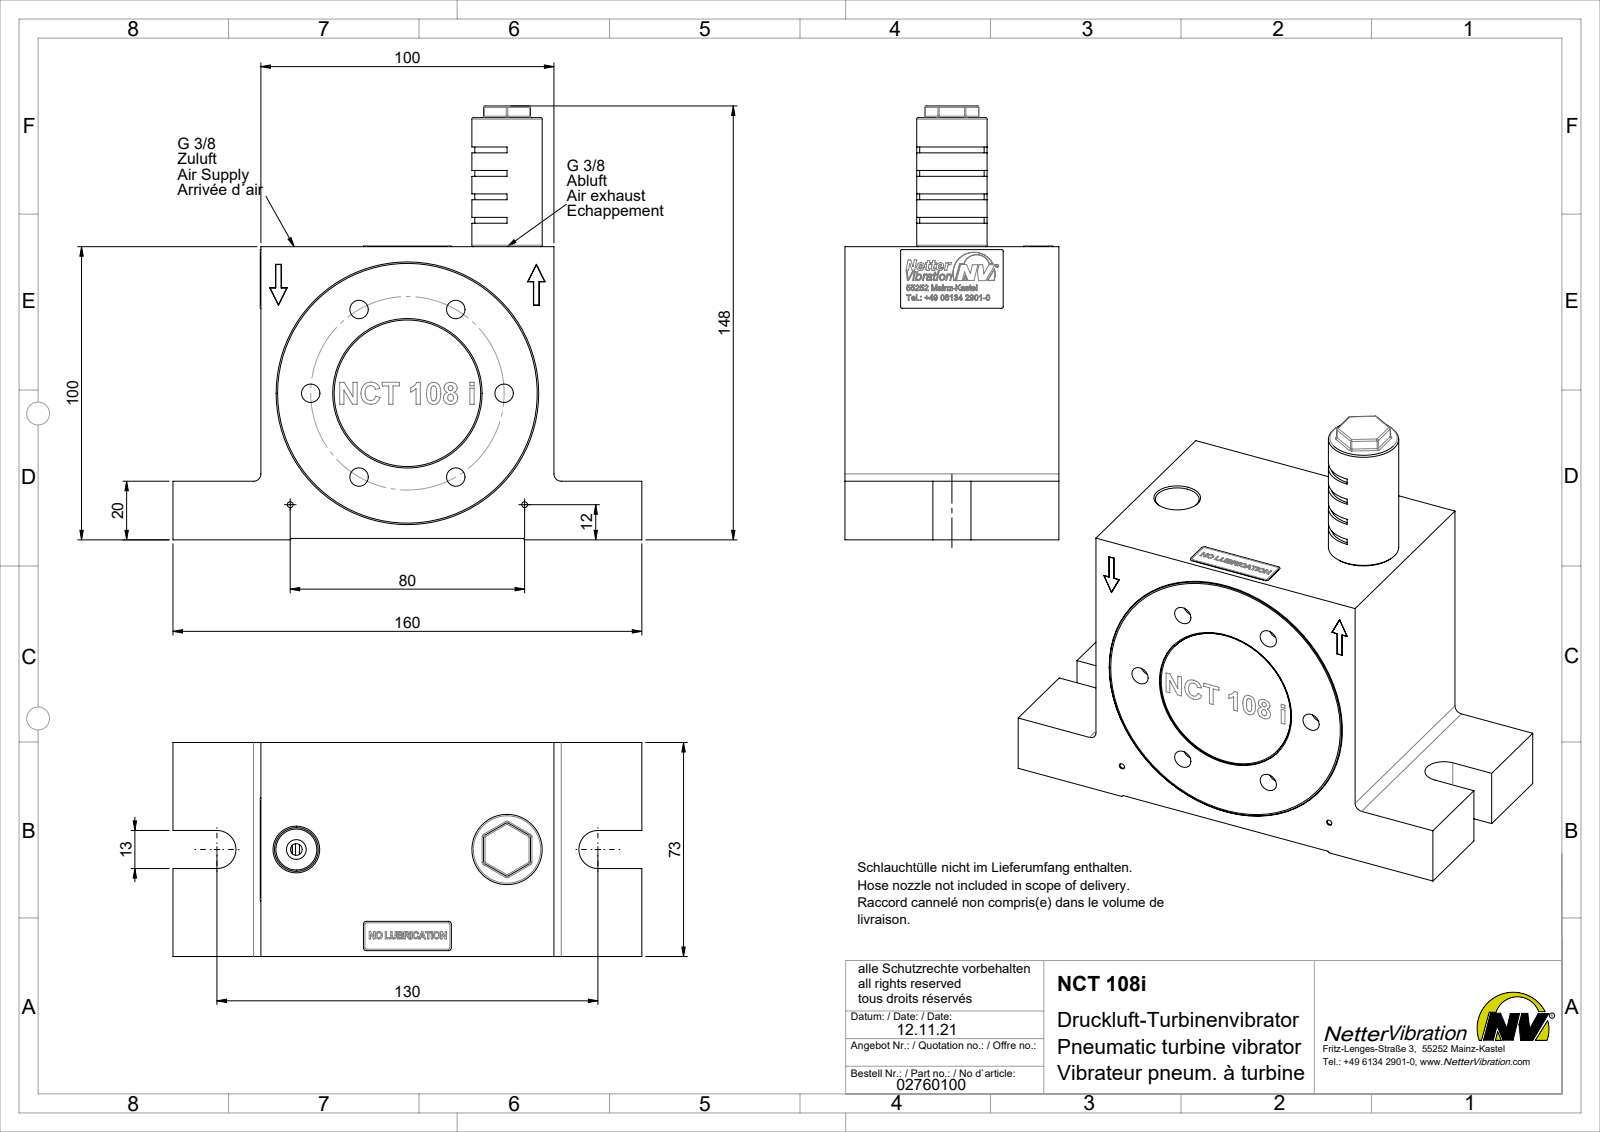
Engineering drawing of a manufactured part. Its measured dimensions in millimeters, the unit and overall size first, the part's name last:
Units: millimetres
Overall size (bounding box): 160 × 146 × 73
Round holes (diameter × count): ⌀6.3 ×6, ⌀2 ×2, ⌀15 ×2, ⌀40 ×1, ⌀51 ×1, ⌀52 ×1, ⌀87.5 ×1, ⌀88.4 ×1
Round bosses / shafts (diameter × count): ⌀87.47 ×1, ⌀85.27 ×1, ⌀50 ×1, ⌀24 ×1, ⌀16.66 ×1
Partial cylindrical surfaces — rounded edges, fillets, slot ends (radius × count): R0.5 ×22, R1 ×4, R2.5 ×2, R6.5 ×2, R11 ×1
Main face-to-face distances: 100, 73, 0.5, 99.5, 30, 20, 19.5, 80, 54, 19
Hole centre spacings: 33, 57.16, 66, 25.32, 38.64, 55.17, 57.28, 70.61
Volume: 785 487 mm³ · Surface area: 79 115 mm²
Bodies: 2 solids, 357 faces (215 planar, 81 cylindrical, 61 other)
Part name (STEP PRODUCT): NCT 108i Turbinenvibrator #02760100
STEP written by: SolidWorks 2015 (AUTOMOTIVE_DESIGN)
